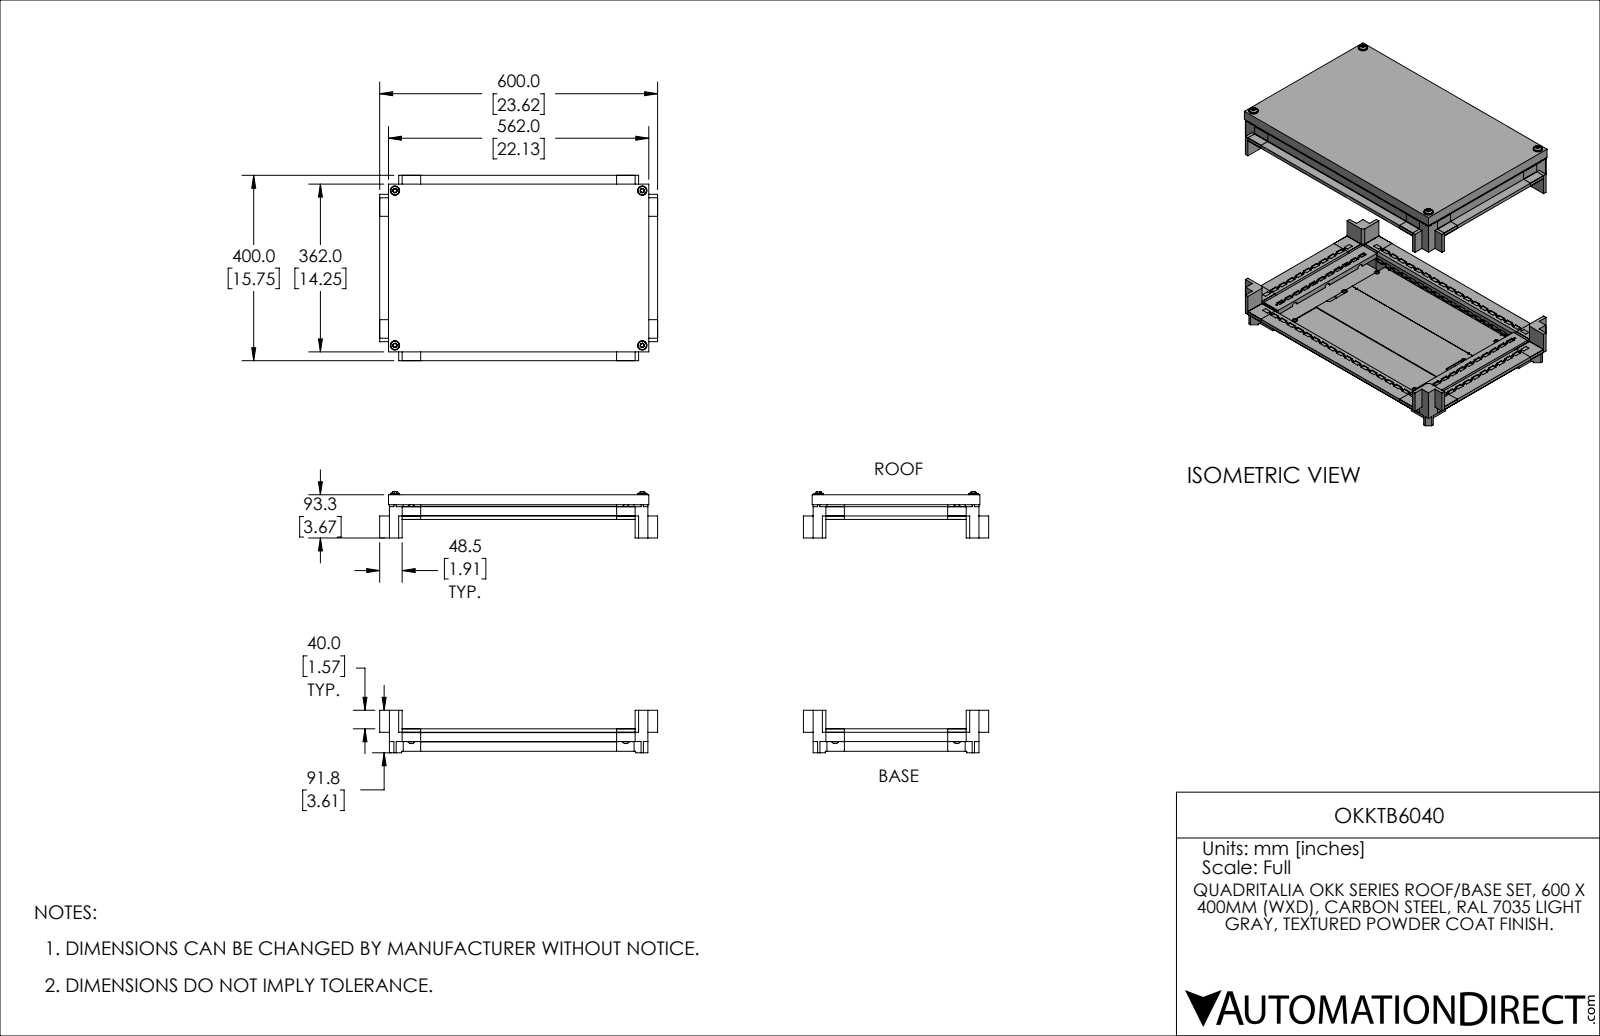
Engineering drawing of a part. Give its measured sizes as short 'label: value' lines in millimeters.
name: OKKTB6040
written by: SolidWorks 2021 (AUTOMOTIVE_DESIGN)
unit: mm
bodies: 59 solids, 3639 faces (2714 planar, 766 cylindrical, 159 other)
size: 600 × 563 × 400
volume: 5 622 000 mm³; area: 1 926 000 mm²
holes: 156× ⌀4.2, 11× ⌀9, 8× ⌀3.9, 4× ⌀13.5, 3× ⌀4.9, 3× ⌀8.2
bosses: 11× ⌀14, 11× ⌀8, 9× ⌀10, 6× ⌀5, 4× ⌀20, 4× ⌀12, 4× ⌀6, 1× ⌀7
rounds: 264× R0.5, 24× R1, 16× R0.3, 12× R4.5, 10× R0.8, 8× R3.5, 6× R5.5, 3× R7
face distances: 1.5, 20, 530, 27.5, 7.5, 531.5, 2.5, 20.5, 17.5, 26.5
hole spacings: 25, 50, 75, 100, 125, 487.4, 150, 489.3
